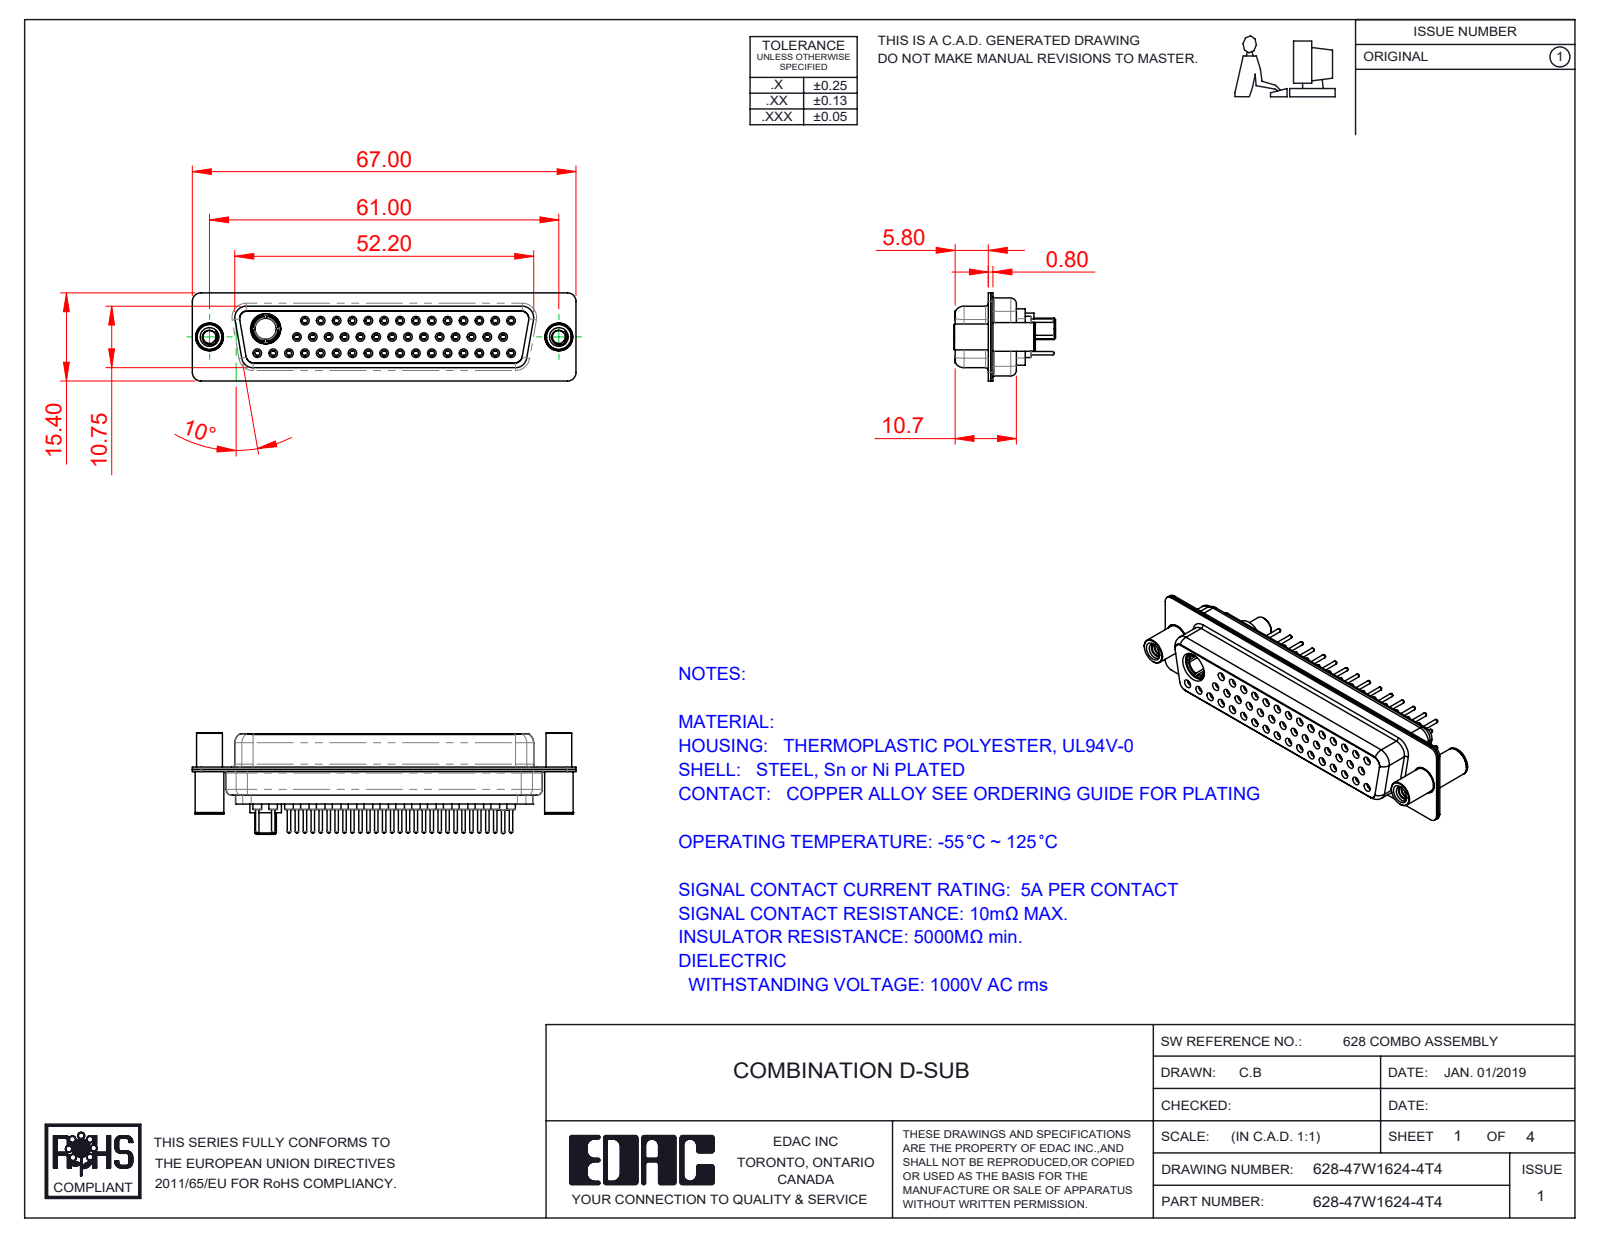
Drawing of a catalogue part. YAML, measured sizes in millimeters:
part_name: "628Combo Housing_47W1; 628Combo Contact Row 3_24; 628Combo Contact Row 2_24; 628Combo Shell Front_50 Contacts (+5 more)"
step_written_by: "SolidWorks 2016 (CONFIG_CONTROL_DESIGN)"
units: millimeters
bodies: {solids: 53, faces: 2957, planar: 789, cylindrical: 1078, other: 1090}
overall_size: [67, 17.75, 15.4]
volume: 7391
surface_area: 15230
round_holes:
  - {diameter: 1.1, count: 46}
  - {diameter: 0.9, count: 45}
  - {diameter: 1.5, count: 45}
  - {diameter: 2, count: 45}
  - {diameter: 1.6, count: 31}
  - {diameter: 1.7, count: 14}
  - {diameter: 4.85, count: 3}
  - {diameter: 2.26, count: 2}
  - {diameter: 3.26, count: 2}
  - {diameter: 4, count: 2}
  - {diameter: 4.05, count: 2}
  - {diameter: 3.7, count: 1}
round_bosses_or_shafts:
  - {diameter: 2.2, count: 46}
  - {diameter: 0.6, count: 46}
  - {diameter: 1.6, count: 15}
  - {diameter: 5, count: 2}
  - {diameter: 4.95, count: 2}
  - {diameter: 4.8, count: 2}
  - {diameter: 4.5, count: 2}
  - {diameter: 5.5, count: 1}
partial_cylinders:
  - {radius: 1.5, count: 16}
  - {radius: 1.35, count: 12}
  - {radius: 2, count: 12}
  - {radius: 1.6, count: 8}
  - {radius: 0.25, count: 4}
  - {radius: 0.5, count: 4}
  - {radius: 0.6, count: 4}
  - {radius: 0.65, count: 4}
face_to_face_distances: [0.4, 11.33, 6.45, 6.05, 1.87, 12.25, 6.2, 5.8, 10.35, 10.93]
hole_center_spacings: [3.16, 2.77, 5.54, 8.31, 11.08, 13.85, 16.62, 19.39]
